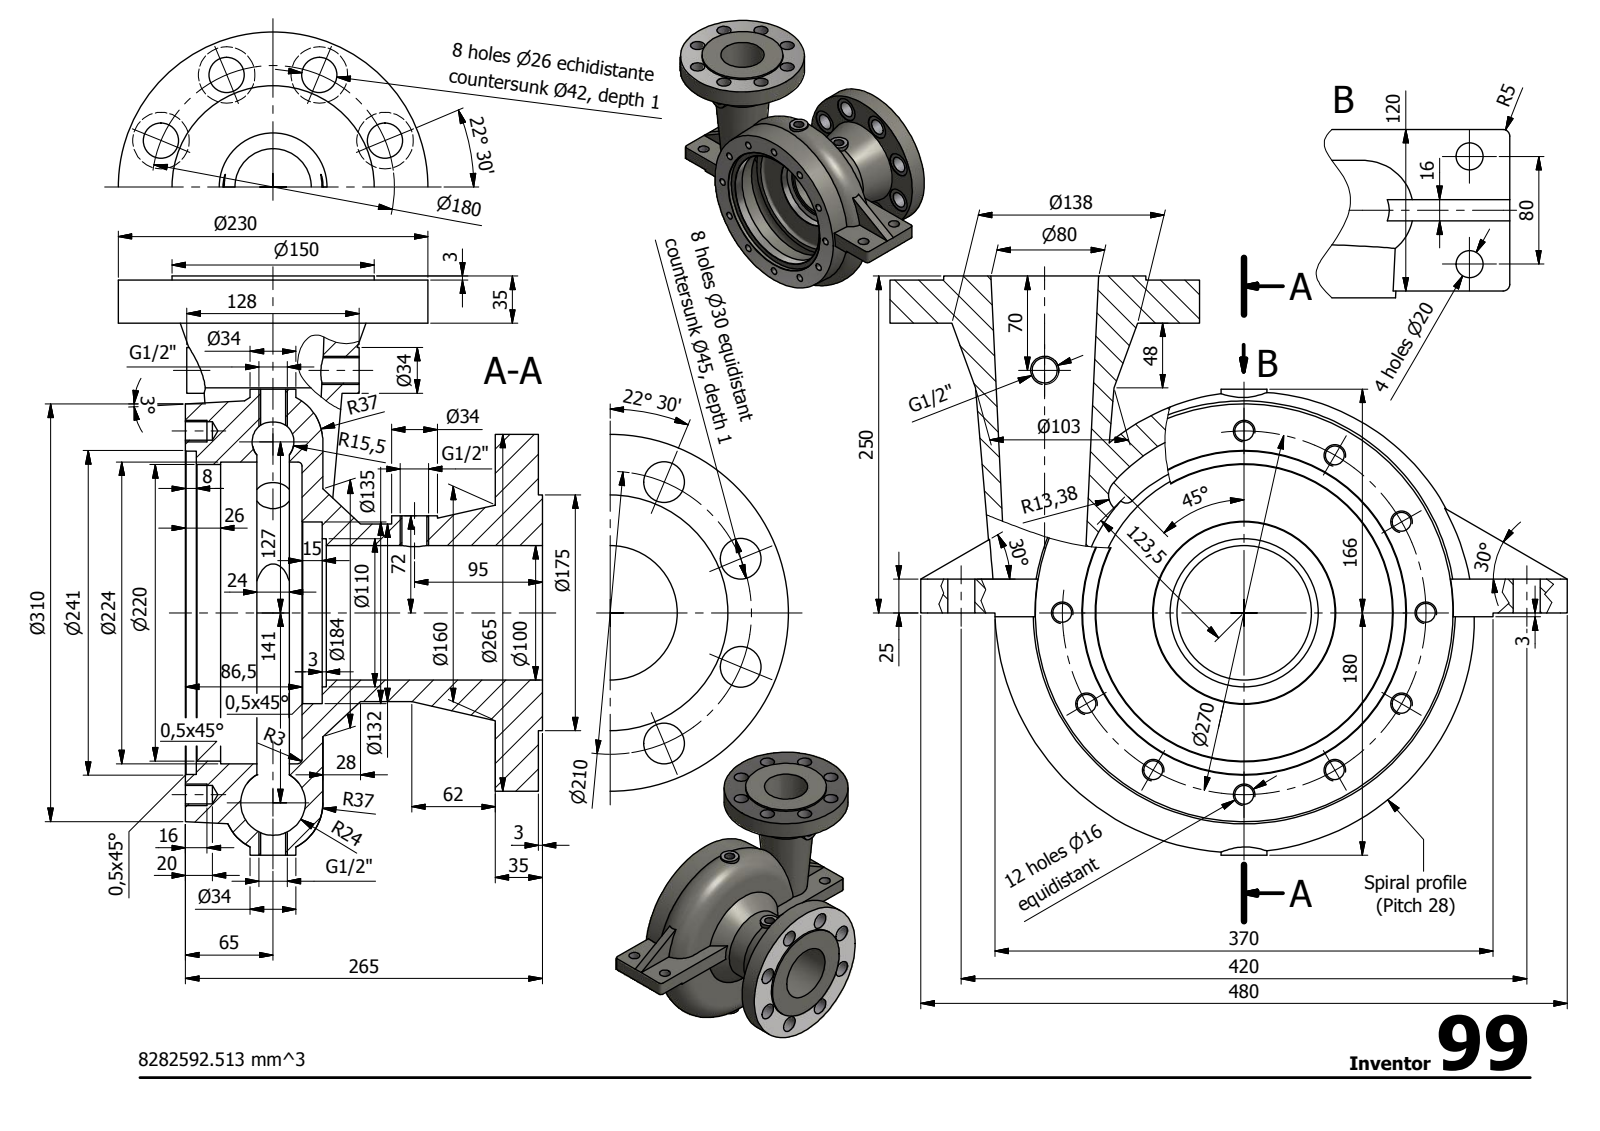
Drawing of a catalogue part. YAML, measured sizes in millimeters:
part_name: "Corp pompa centrifugala (Inv2011)"
step_written_by: "Autodesk Inventor 2014 (AUTOMOTIVE_DESIGN)"
units: millimeters
bodies: {solids: 1, faces: 159, planar: 57, cylindrical: 75, other: 27}
overall_size: [503, 430, 315]
volume: 8284000
surface_area: 887879
round_holes:
  - {diameter: 13.84, count: 12}
  - {diameter: 26, count: 8}
  - {diameter: 30, count: 8}
  - {diameter: 42, count: 8}
  - {diameter: 45, count: 8}
  - {diameter: 20, count: 4}
  - {diameter: 18.63, count: 3}
  - {diameter: 100, count: 1}
  - {diameter: 110, count: 1}
  - {diameter: 135, count: 1}
  - {diameter: 220, count: 1}
  - {diameter: 224, count: 1}
round_bosses_or_shafts:
  - {diameter: 34, count: 3}
  - {diameter: 265, count: 1}
  - {diameter: 230, count: 1}
  - {diameter: 175, count: 1}
  - {diameter: 150, count: 1}
  - {diameter: 132, count: 1}
partial_cylinders:
  - {radius: 5, count: 4}
  - {radius: 123.5, count: 1}
face_to_face_distances: [3, 32, 35, 262, 222, 230, 86.5, 175.5, 143.5, 250]
hole_center_spacings: [135, 69.88, 260.8, 105, 33.8, 55.3, 82.21, 109.5]
